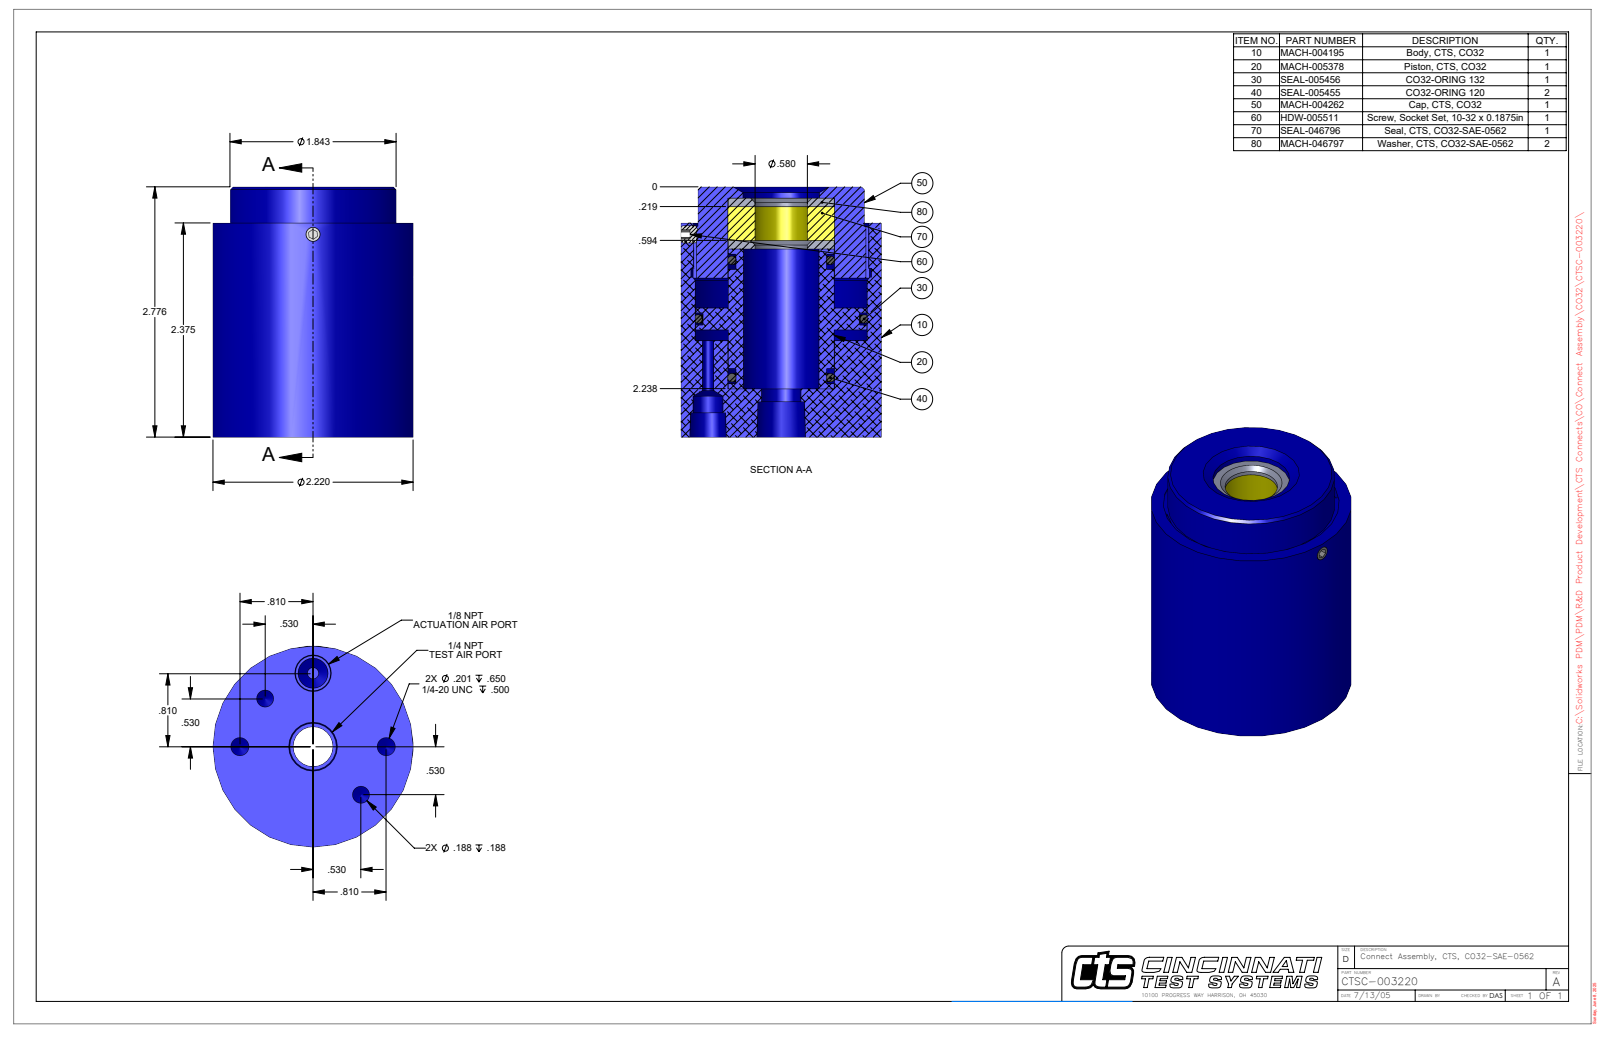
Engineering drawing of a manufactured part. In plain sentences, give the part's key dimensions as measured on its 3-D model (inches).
The part is named "CTSC-003220". Its 3-D file was written by "SolidWorks 2023 (AUTOMOTIVE_DESIGN)". It is 1 solid with 118 faces: 49 planar, 44 cylindrical and 25 other. Overall it measures 2.776 by 2.22 by 2.22 inches. Its volume is 8.949 cubic inches and its surface area 35.56 square inches. Round holes: 2 of diameter 0.187, 2 of diameter 0.201, 1 of diameter 0.094, 1 of diameter 0.125, 1 of diameter 0.159, 1 of diameter 0.332, 1 of diameter 0.438, 1 of diameter 0.58, 1 of diameter 0.837, 1 of diameter 0.848, 1 of diameter 1.182, 1 of diameter 1.943. Round bosses or shafts: 1 of diameter 2.22, 1 of diameter 1.843, 1 of diameter 1.172. Partial cylindrical surfaces (rounded edges, fillets, slot ends): 1 of radius 0.095, 1 of radius 1.092. The main face-to-face distances are 2.776, 2.375, 0.401, 0.537, 1.837, 2.238, 2.087, 1.55, 0.287, 0.688. The hole center spacings are 0.6, 0.81, 1.441, 0.75, 1.145, 1.5, 1.62.
